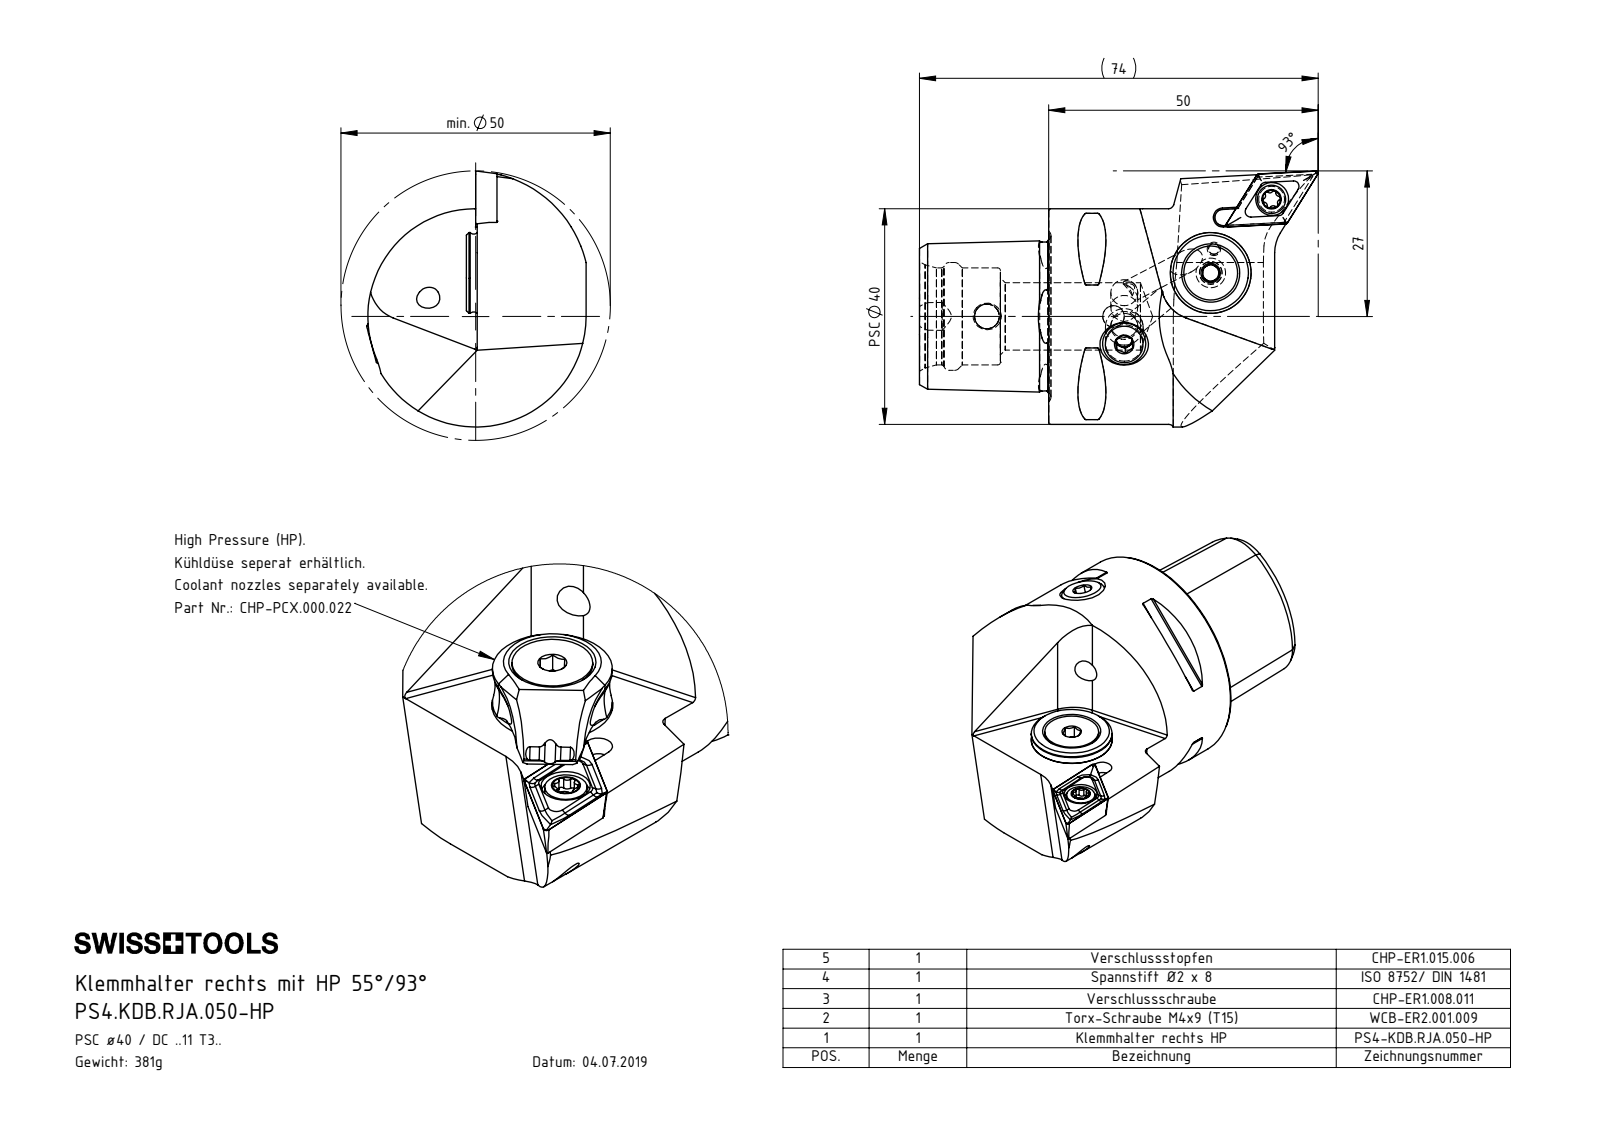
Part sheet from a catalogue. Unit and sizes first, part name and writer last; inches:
Units: inches
Overall size (bounding box): 2.914 × 1.87 × 1.603
Round holes (diameter × count): ⌀0.165 ×3, ⌀0.047 ×1, ⌀0.079 ×1, ⌀0.098 ×1, ⌀0.118 ×1, ⌀0.13 ×1, ⌀0.157 ×1, ⌀0.173 ×1, ⌀0.181 ×1, ⌀0.197 ×1, ⌀0.205 ×1, ⌀0.24 ×1
Round bosses / shafts (diameter × count): ⌀1.575 ×1, ⌀0.591 ×1, ⌀0.528 ×1, ⌀0.394 ×1, ⌀0.315 ×1, ⌀0.217 ×1, ⌀0.207 ×1, ⌀0.197 ×1
Partial cylindrical surfaces — rounded edges, fillets, slot ends (radius × count): R0.012 ×8, R0.013 ×6, R0.023 ×6, R0.02 ×2, R0.276 ×2, R0.059 ×1, R0.118 ×1, R0.807 ×1
Main face-to-face distances: 0.177, 0.618, 0.795, 0.945, 0.651, 0.033, 0.144, 0.611, 1.39, 0.591
Hole centre spacings: 0.177, 0.556, 0.561, 0.698, 0.703, 0.778, 0.884, 0.925
Volume: 2.969 in³ · Surface area: 23.49 in²
Bodies: 8 solids, 386 faces (91 planar, 100 cylindrical, 195 other)
Part name (STEP PRODUCT): ISO 8752 2x8; CHP-ER1.015.006_A; WCB-ER2.001.009_A; DIN 7991 - M5x15 (+6 more)
STEP written by: SolidWorks 2017 (AUTOMOTIVE_DESIGN)
